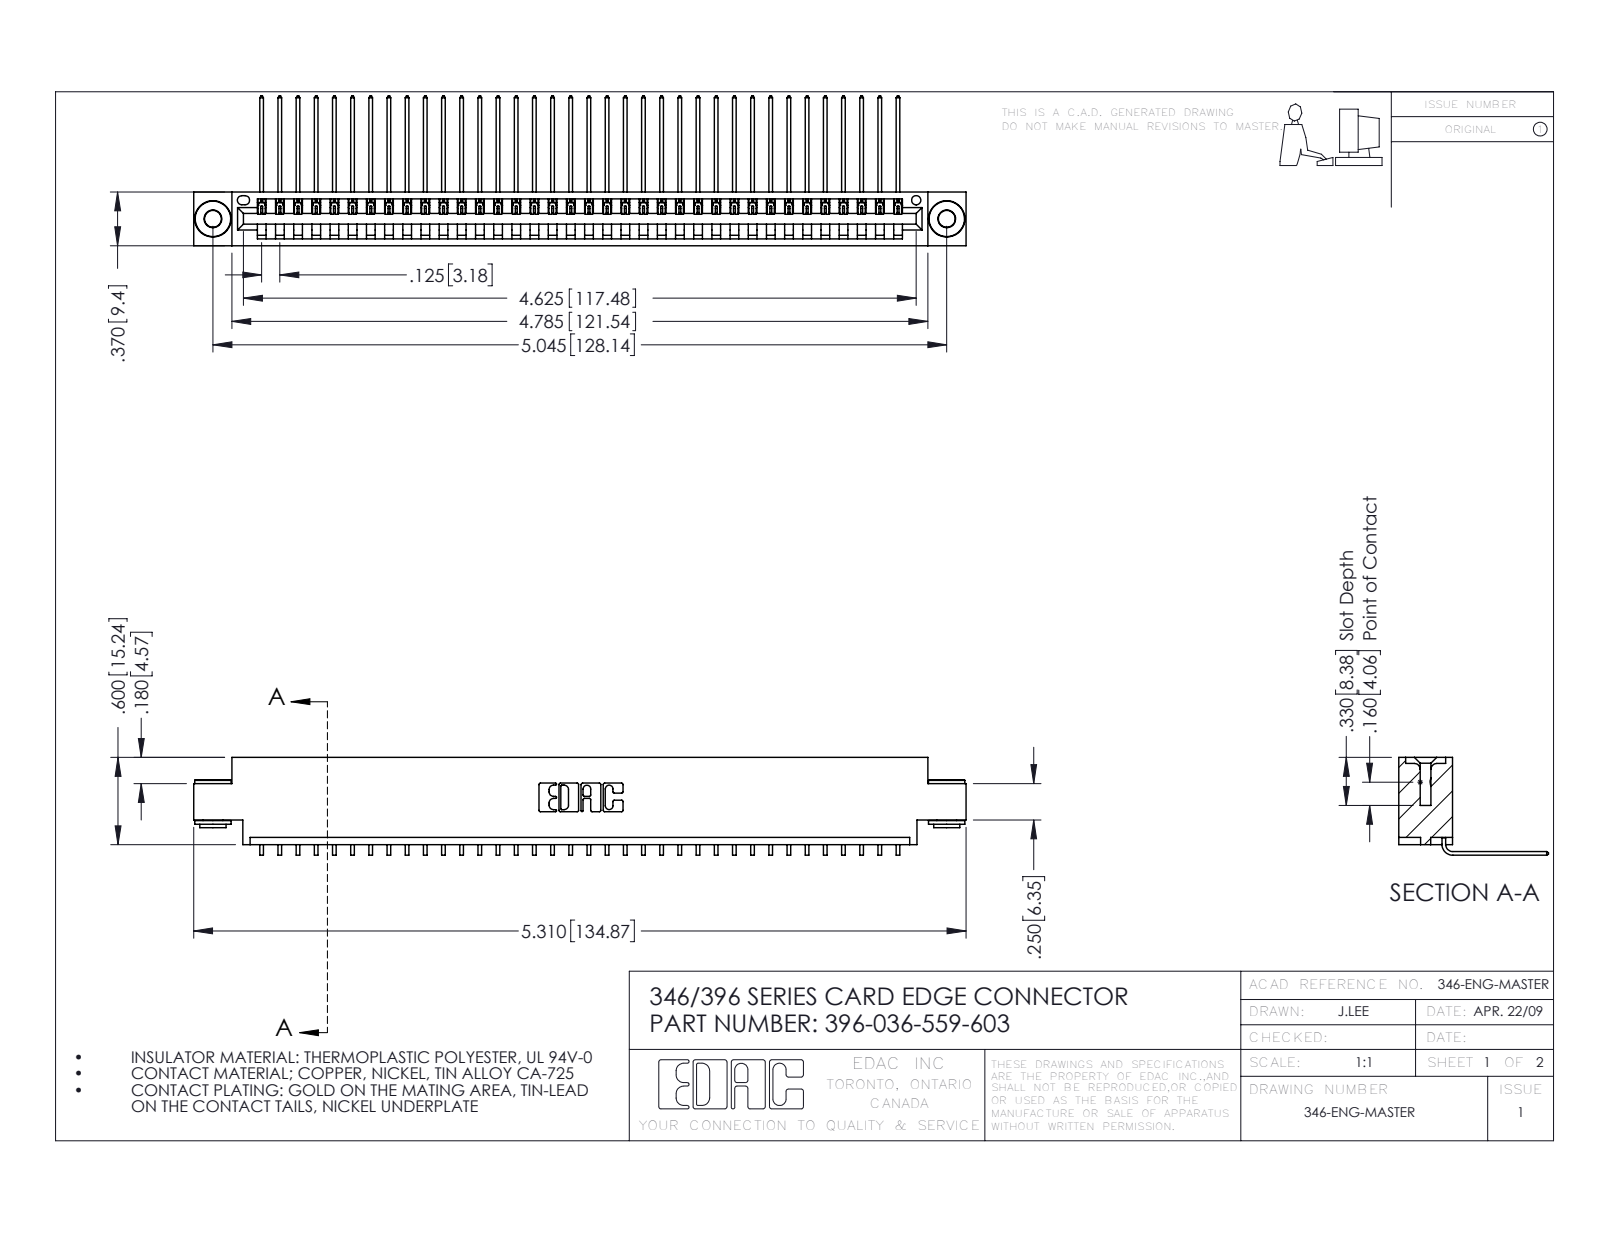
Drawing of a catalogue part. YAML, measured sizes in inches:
part_name: "346 Part_0.170 Offset - 0.156 Dia-TH; 396-036-559-603; 345-250-002_345-250-002-102; 345-292-001_558 559 Tail - 1"
step_written_by: "SolidWorks 2016 (CONFIG_CONTROL_DESIGN)"
units: inches
bodies: {solids: 39, faces: 2324, planar: 1602, cylindrical: 714, other: 8}
overall_size: [5.31, 1.03, 0.673]
volume: 0.784
surface_area: 26.5
round_holes:
  - {diameter: 0.116, count: 2}
  - {diameter: 0.156, count: 2}
  - {diameter: 0.064, count: 1}
round_bosses_or_shafts:
  - {diameter: 0.25, count: 2}
  - {diameter: 0.18, count: 2}
  - {diameter: 0.136, count: 2}
partial_cylinders:
  - {radius: 0.006, count: 72}
  - {radius: 0.01, count: 22}
  - {radius: 0.007, count: 6}
  - {radius: 0.031, count: 6}
  - {radius: 0.026, count: 3}
  - {radius: 0.031, count: 2}
  - {radius: 0.04, count: 2}
  - {radius: 0.014, count: 1}
face_to_face_distances: [0.048, 0.322, 0.37, 0.025, 0.25, 0.072, 0.298, 0.148, 0.222, 0.1]
hole_center_spacings: [0.246, 4.836, 5.045]
